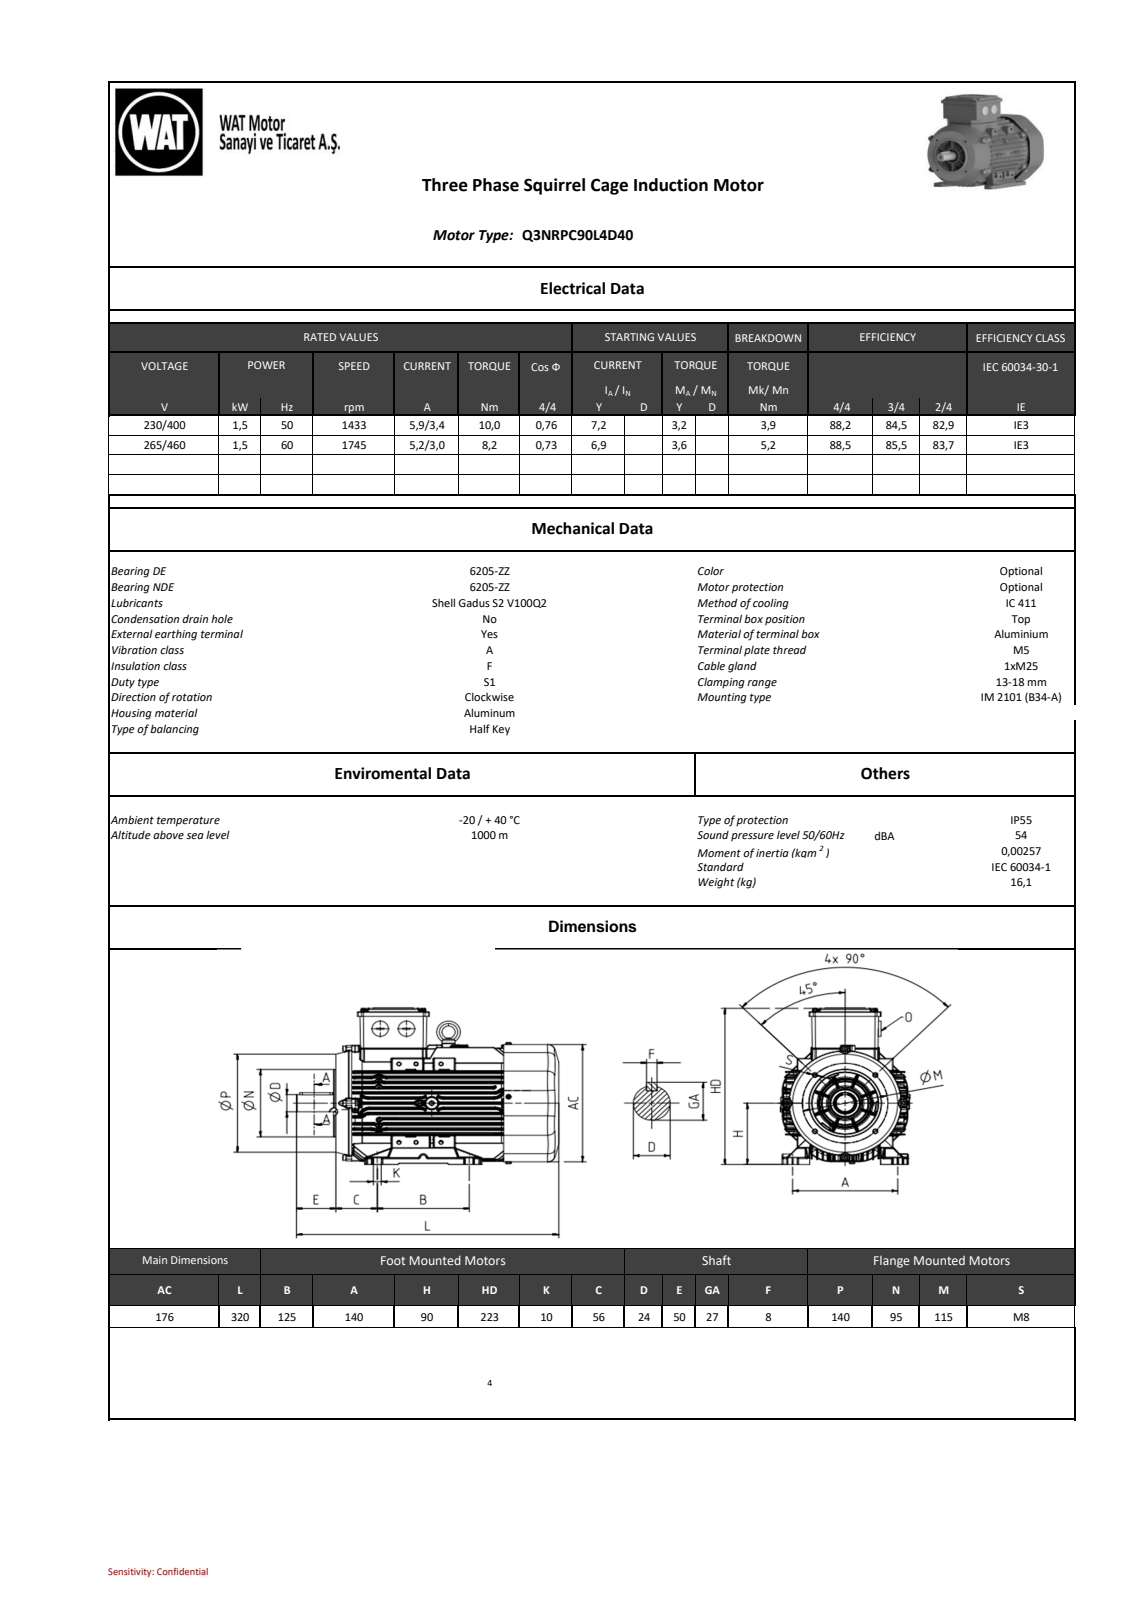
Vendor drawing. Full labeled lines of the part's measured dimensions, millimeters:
Part name (STEP PRODUCT): C9012118CE057q2d
STEP written by: SIEMENS PLM Software NX 11.0 (AUTOMOTIVE_DESIGN)
Units: millimetres
Bodies: 0 solids, 15080 faces (3690 planar, 4556 cylindrical, 6834 other)
Overall size (bounding box): 320 × 210 × 180
Round holes (diameter × count): ⌀4.2 ×6, ⌀5.1 ×6, ⌀9 ×6, ⌀6.8 ×4, ⌀12 ×4, ⌀2 ×2, ⌀2.5 ×2, ⌀3 ×2, ⌀7 ×2, ⌀4 ×1, ⌀8 ×1, ⌀12.2 ×1
Round bosses / shafts (diameter × count): ⌀5 ×12, ⌀8 ×8, ⌀4 ×8, ⌀9.4 ×6, ⌀9.2 ×6, ⌀8.5 ×6, ⌀25 ×3, ⌀35 ×2
Partial cylindrical surfaces — rounded edges, fillets, slot ends (radius × count): R0.5 ×1186, R1 ×714, R0.8 ×511, R0.2 ×176, R0.3 ×168, R1.5 ×119, R4 ×88, R0.6 ×72
Main face-to-face distances: 4.49, 4.48, 4.5, 4.79, 4.19, 4.78, 4.18, 0.8, 105, 0.31
Hole centre spacings: 20, 81, 14.14, 14.15, 28.28, 37.75, 57.28, 57.5
